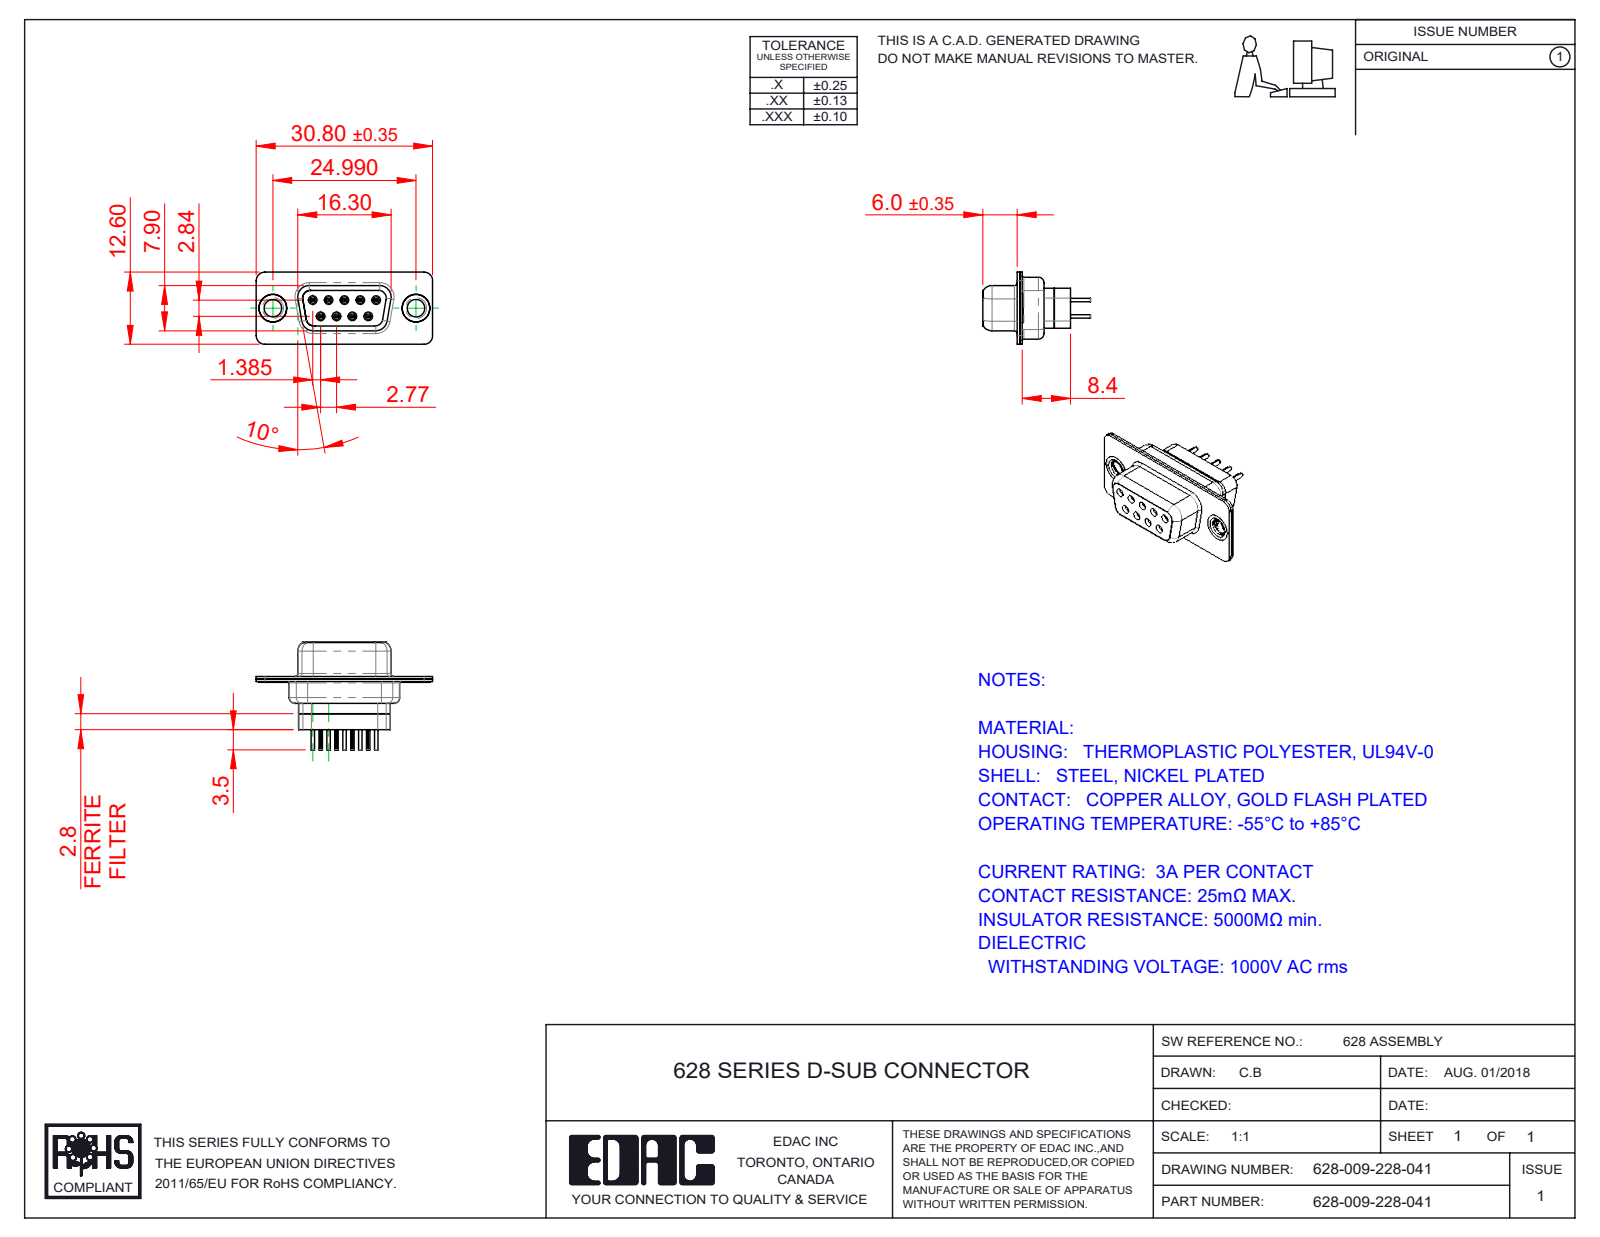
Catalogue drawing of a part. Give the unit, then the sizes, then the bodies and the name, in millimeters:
Units: millimetres
Overall size (bounding box): 30.8 × 18.8 × 12.6
Round holes (diameter × count): ⌀0.2 ×9, ⌀0.8 ×9, ⌀0.9 ×9, ⌀1.1 ×9, ⌀1.6 ×9, ⌀1.7 ×5, ⌀3.05 ×2, ⌀4 ×2, ⌀4.05 ×2, ⌀4.85 ×2
Round bosses / shafts (diameter × count): ⌀2 ×9, ⌀1.5 ×9, ⌀1.2 ×9, ⌀0.6 ×9, ⌀5 ×2, ⌀4.95 ×2, ⌀4.8 ×2, ⌀3.55 ×2
Partial cylindrical surfaces — rounded edges, fillets, slot ends (radius × count): R0.1 ×18, R1.5 ×17, R2 ×12, R0.28 ×9, R1.35 ×6, R0.25 ×4, R0.5 ×4, R0.6 ×4
Main face-to-face distances: 0.45, 0.4, 0.9, 6.05, 5.6, 6.5, 8.85, 6.6, 8.4, 8.5
Hole centre spacings: 3.16, 2.77, 5.54, 5.03, 5.04, 8.31, 7.48, 7.49
Volume: 1 924 mm³ · Surface area: 4 823 mm²
Bodies: 15 solids, 1425 faces (352 planar, 441 cylindrical, 632 other)
Part name (STEP PRODUCT): 628 Shell Front_09 Contacts; 628 Thru Hole Rivet; 628 Shell Rear_09 Contacts; 628-009-228-041 (+3 more)
STEP written by: SolidWorks 2020 (CONFIG_CONTROL_DESIGN)
